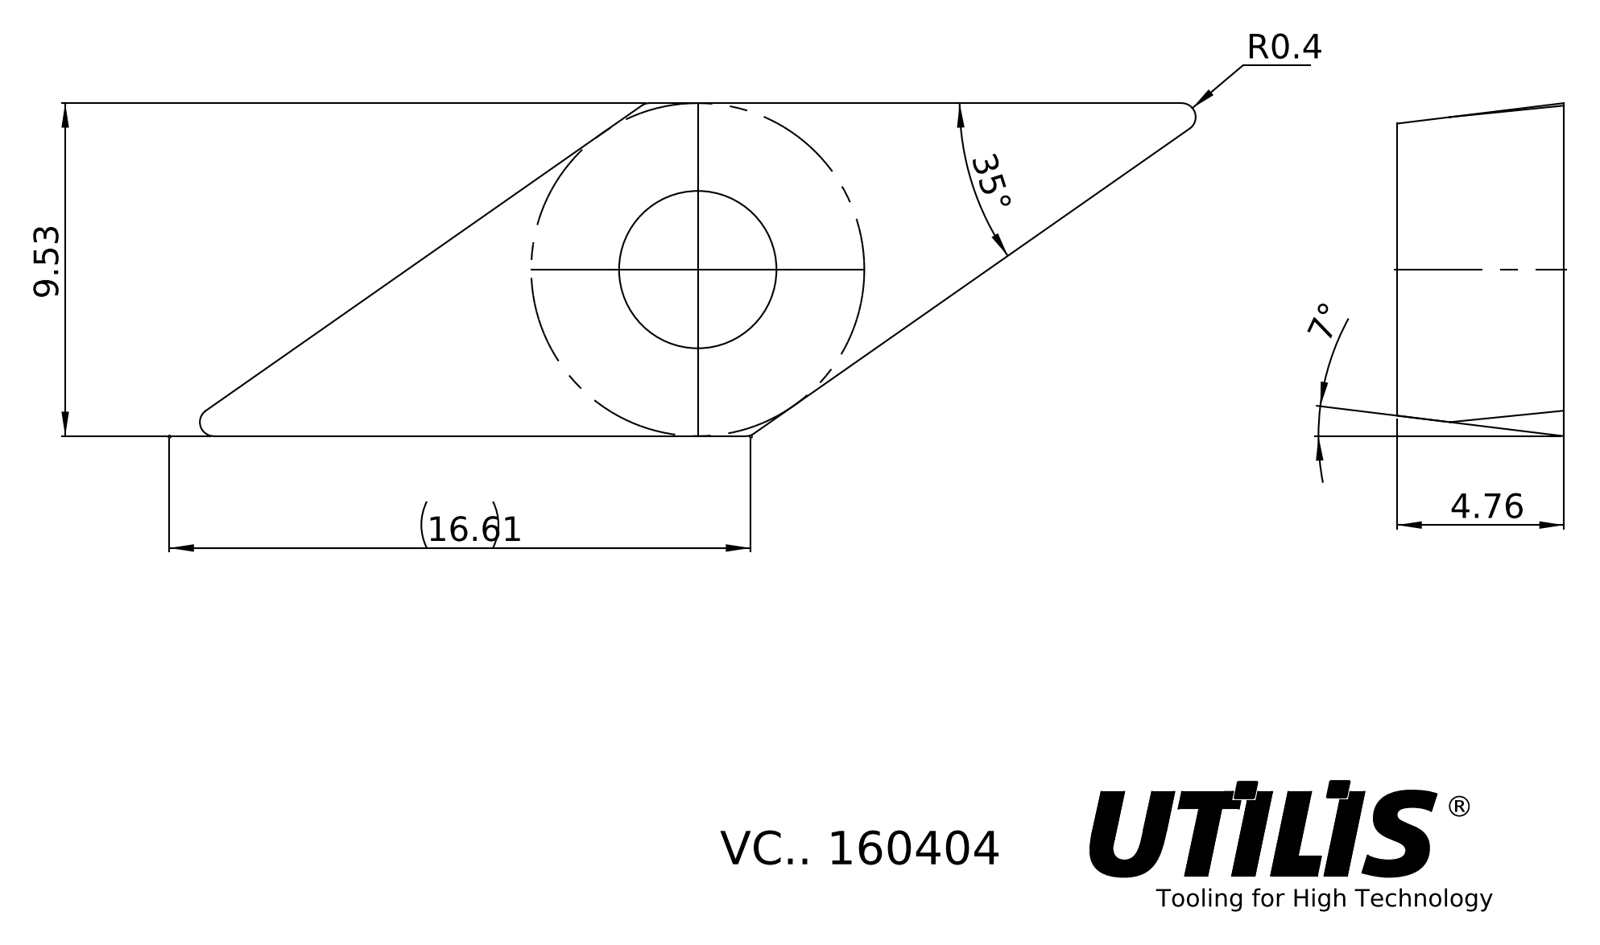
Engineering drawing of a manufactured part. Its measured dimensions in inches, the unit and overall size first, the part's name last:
Units: inches
Overall size (bounding box): 1.121 × 0.375 × 0.187
Round holes (diameter × count): ⌀0.177 ×1
Main face-to-face distances: 0.187
Volume: 0.036 in³ · Surface area: 0.944 in²
Bodies: 1 solid, 13 faces (2 planar, 2 cylindrical, 9 other)
Part name (STEP PRODUCT): VC.. 160404
STEP written by: SolidWorks 2016 (AUTOMOTIVE_DESIGN)
